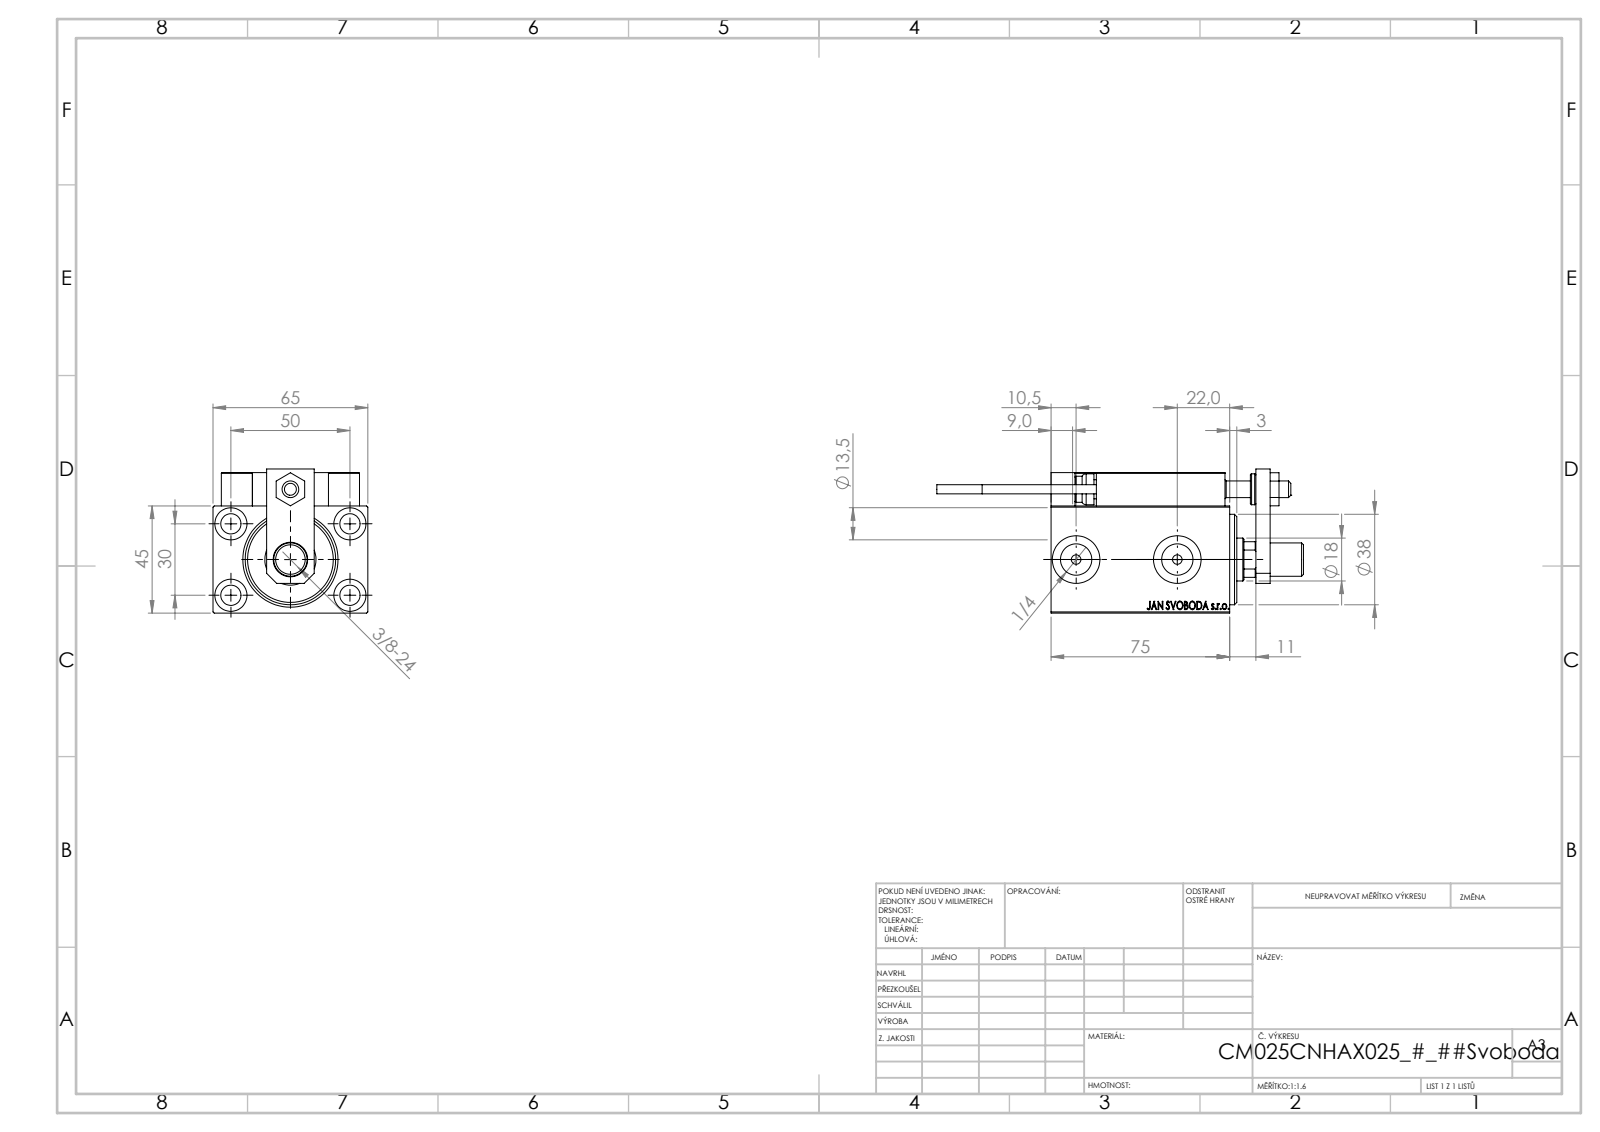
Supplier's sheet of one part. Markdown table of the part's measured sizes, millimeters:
| quantity | value |
| --- | --- |
| part name | TYC_L79; MAGNET; V450CM_MALE_METRIC; V450CM_C_VCP (+7 more) |
| STEP written by | SolidWorks 2019 (CONFIG_CONTROL_DESIGN) |
| units | millimeters |
| bodies | 24 solids, 1295 faces (563 planar, 192 cylindrical, 540 other) |
| overall size | 154 × 65 × 60.5 |
| volume | 238 637 mm³ |
| surface area | 72 791 mm² |
| round holes (diameter × count) | 4 × 6, 8 × 5, 8.5 × 5, 3.2 × 4, 13.5 × 4, 5 × 2, 13.16 × 2, 20 × 2, 7 × 1, 14.5 × 1, 18 × 1, 21.5 × 1 |
| round bosses / shafts (diameter × count) | 5 × 2, 3.8 × 2, 14 × 1, 13 × 1, 12 × 1, 11 × 1 |
| partial cylindrical surfaces (radius × count) | 0.3 × 30, 3 × 2, 8.5 × 1 |
| main face-to-face distances | 45, 14, 65, 6, 59, 13, 3, 19, 3.5, 20 |
| hole center spacings | 29.15, 11.37, 20, 27.07, 28.9, 29.59, 29.69, 30 |
